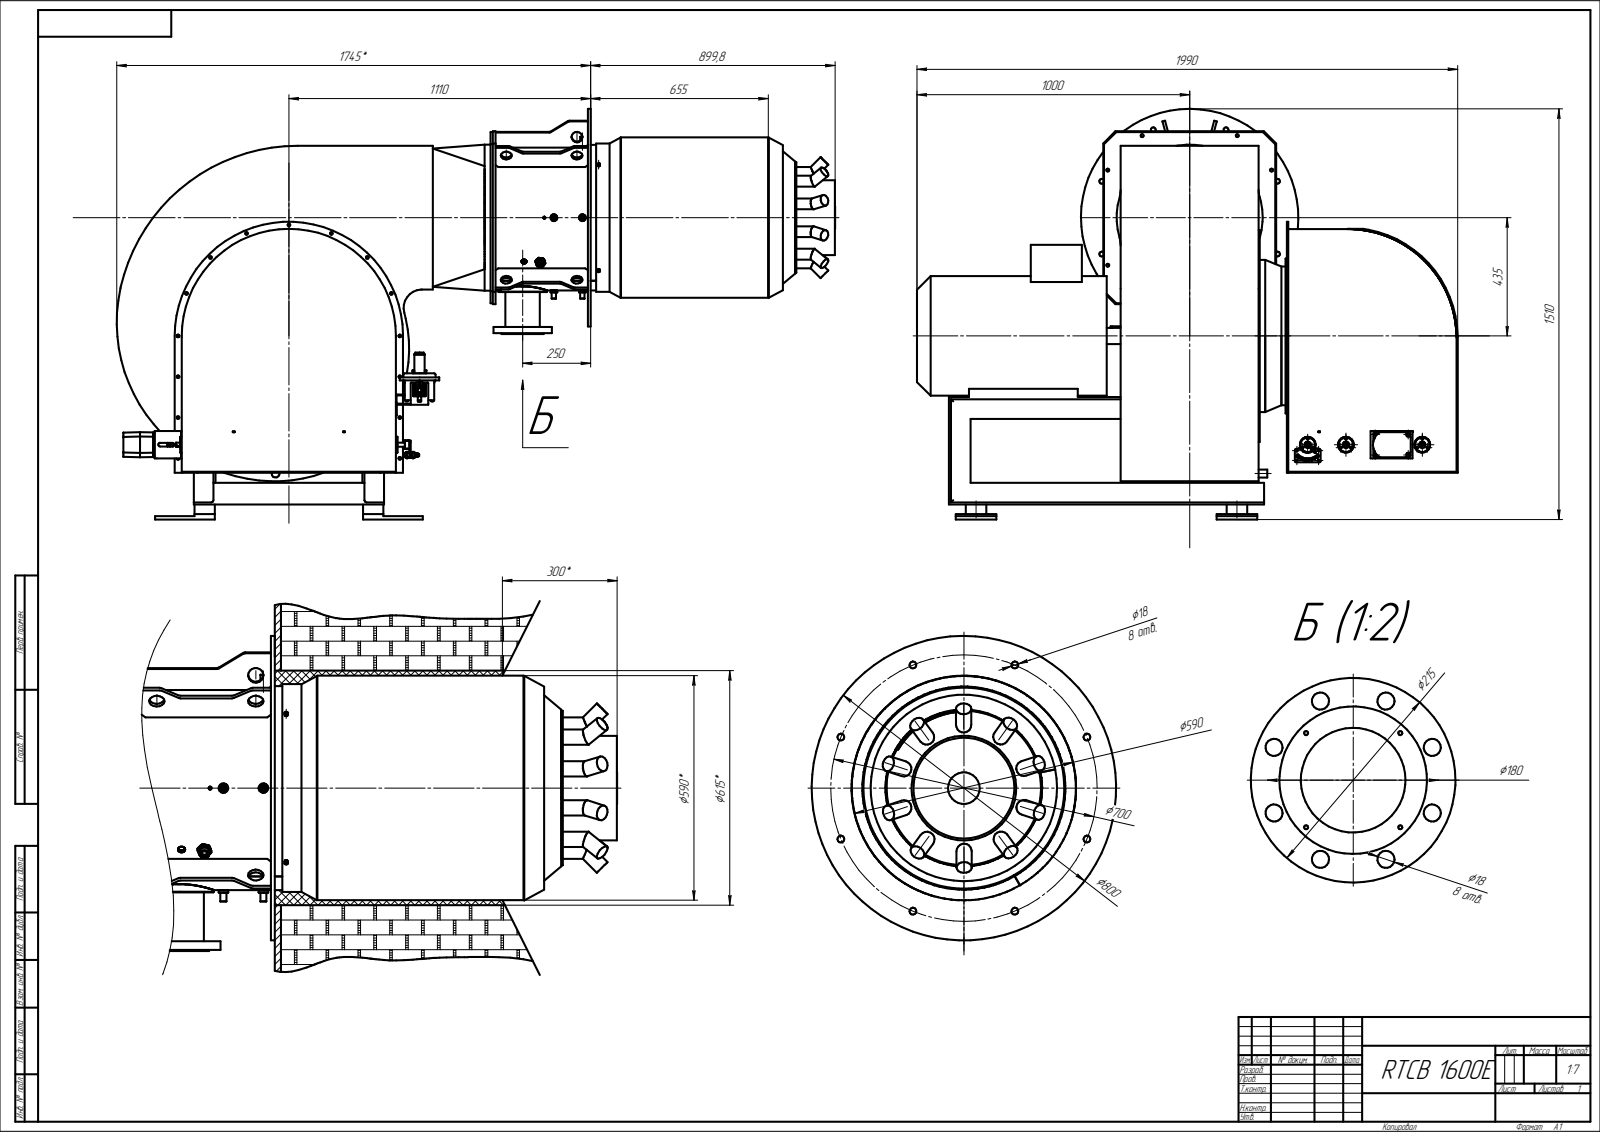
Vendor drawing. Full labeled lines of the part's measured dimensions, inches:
Part name (STEP PRODUCT): PYTG-20E Облегченная
STEP written by: C3D Toolkit (CONFIG_CONTROL_DESIGN)
Units: inches
Bodies: 2 solids, 1044 faces (697 planar, 267 cylindrical, 80 other)
Overall size (bounding box): 104.067 × 78.315 × 59.449
Volume: 72 440 in³ · Surface area: 29 730 in²
Round holes (diameter × count): ⌀0.709 ×8, ⌀4.331 ×1, ⌀5.039 ×1, ⌀10.433 ×1, ⌀21.142 ×1, ⌀21.161 ×1, ⌀21.26 ×1
Round bosses / shafts (diameter × count): ⌀1.575 ×20, ⌀0.63 ×8, ⌀0.315 ×8, ⌀0.394 ×6, ⌀0.591 ×5, ⌀2.953 ×4, ⌀2.283 ×4, ⌀2.047 ×4
Partial cylindrical surfaces — rounded edges, fillets, slot ends (radius × count): R0.374 ×4, R0.413 ×4, R0.236 ×2, R0.315 ×2, R15.748 ×2, R0.118 ×1, R0.896 ×1, R2.362 ×1
Main face-to-face distances: 3.15, 0.157, 20, 28.661, 0.394, 28.819, 24.094, 4.094, 30.787, 48.819
Hole centre spacings: 10.546, 13.78, 19.487, 25.461, 27.559
